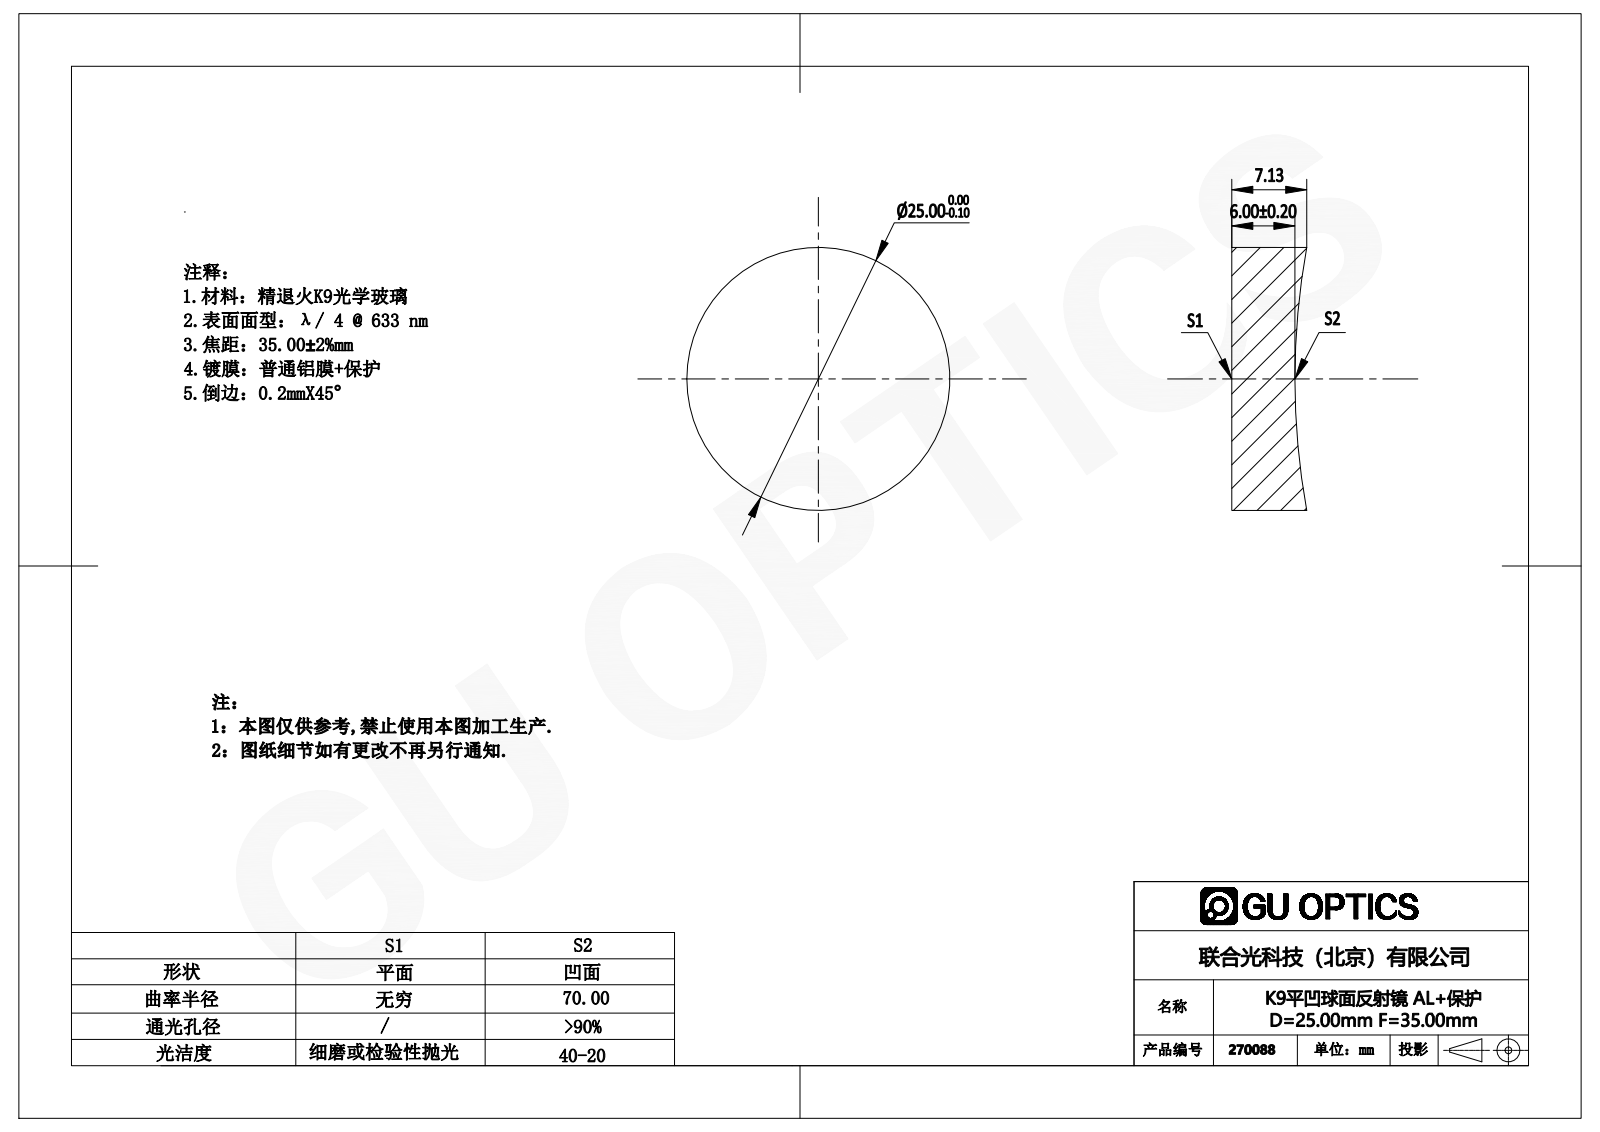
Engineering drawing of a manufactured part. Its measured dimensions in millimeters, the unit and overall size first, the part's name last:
Units: millimetres
Overall size (bounding box): 25 × 25 × 7.12
Round bosses / shafts (diameter × count): ⌀25 ×1
Volume: 3 221 mm³ · Surface area: 1 545 mm²
Bodies: 1 solid, 5 faces (1 planar, 2 cylindrical, 2 other)
Part name (STEP PRODUCT): 270023
STEP written by: SolidWorks 2016 (AUTOMOTIVE_DESIGN)
